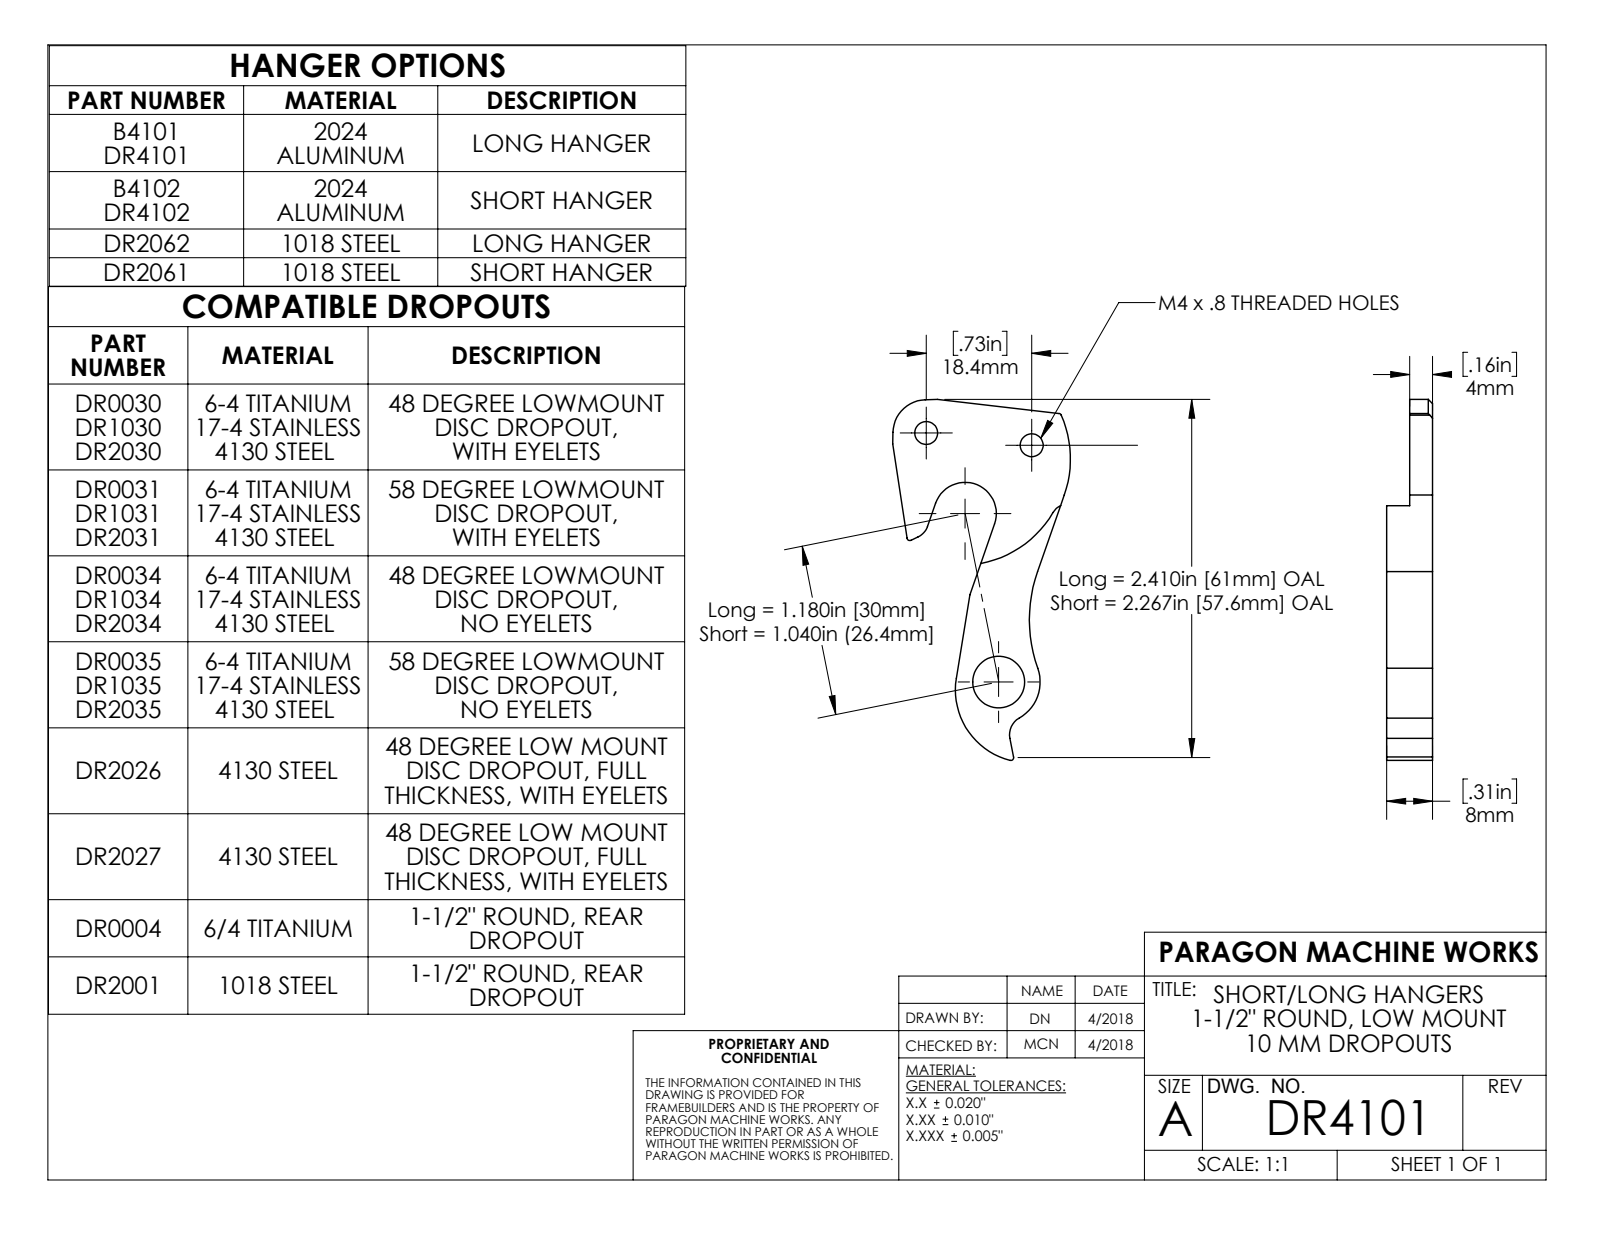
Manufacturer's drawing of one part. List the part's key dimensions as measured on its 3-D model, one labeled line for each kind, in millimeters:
Part name (STEP PRODUCT): DR4001
STEP written by: SolidWorks 2018 (AUTOMOTIVE_DESIGN)
Units: millimetres
Bodies: 1 solid, 41 faces (17 planar, 23 cylindrical, 1 other)
Overall size (bounding box): 63.03 × 31.02 × 8
Volume: 4 950 mm³ · Surface area: 3 278 mm²
Round holes (diameter × count): ⌀4 ×2, ⌀9.04 ×1
Partial cylindrical surfaces — rounded edges, fillets, slot ends (radius × count): R0.51 ×2, R0.51 ×1, R3.05 ×1, R3.17 ×1, R3.3 ×1, R5.46 ×1, R5.81 ×1, R7.24 ×1
Main face-to-face distances: 4, 8, 9.83, 20.75, 10.92
Hole centre spacings: 18.54, 41.73, 45.26
